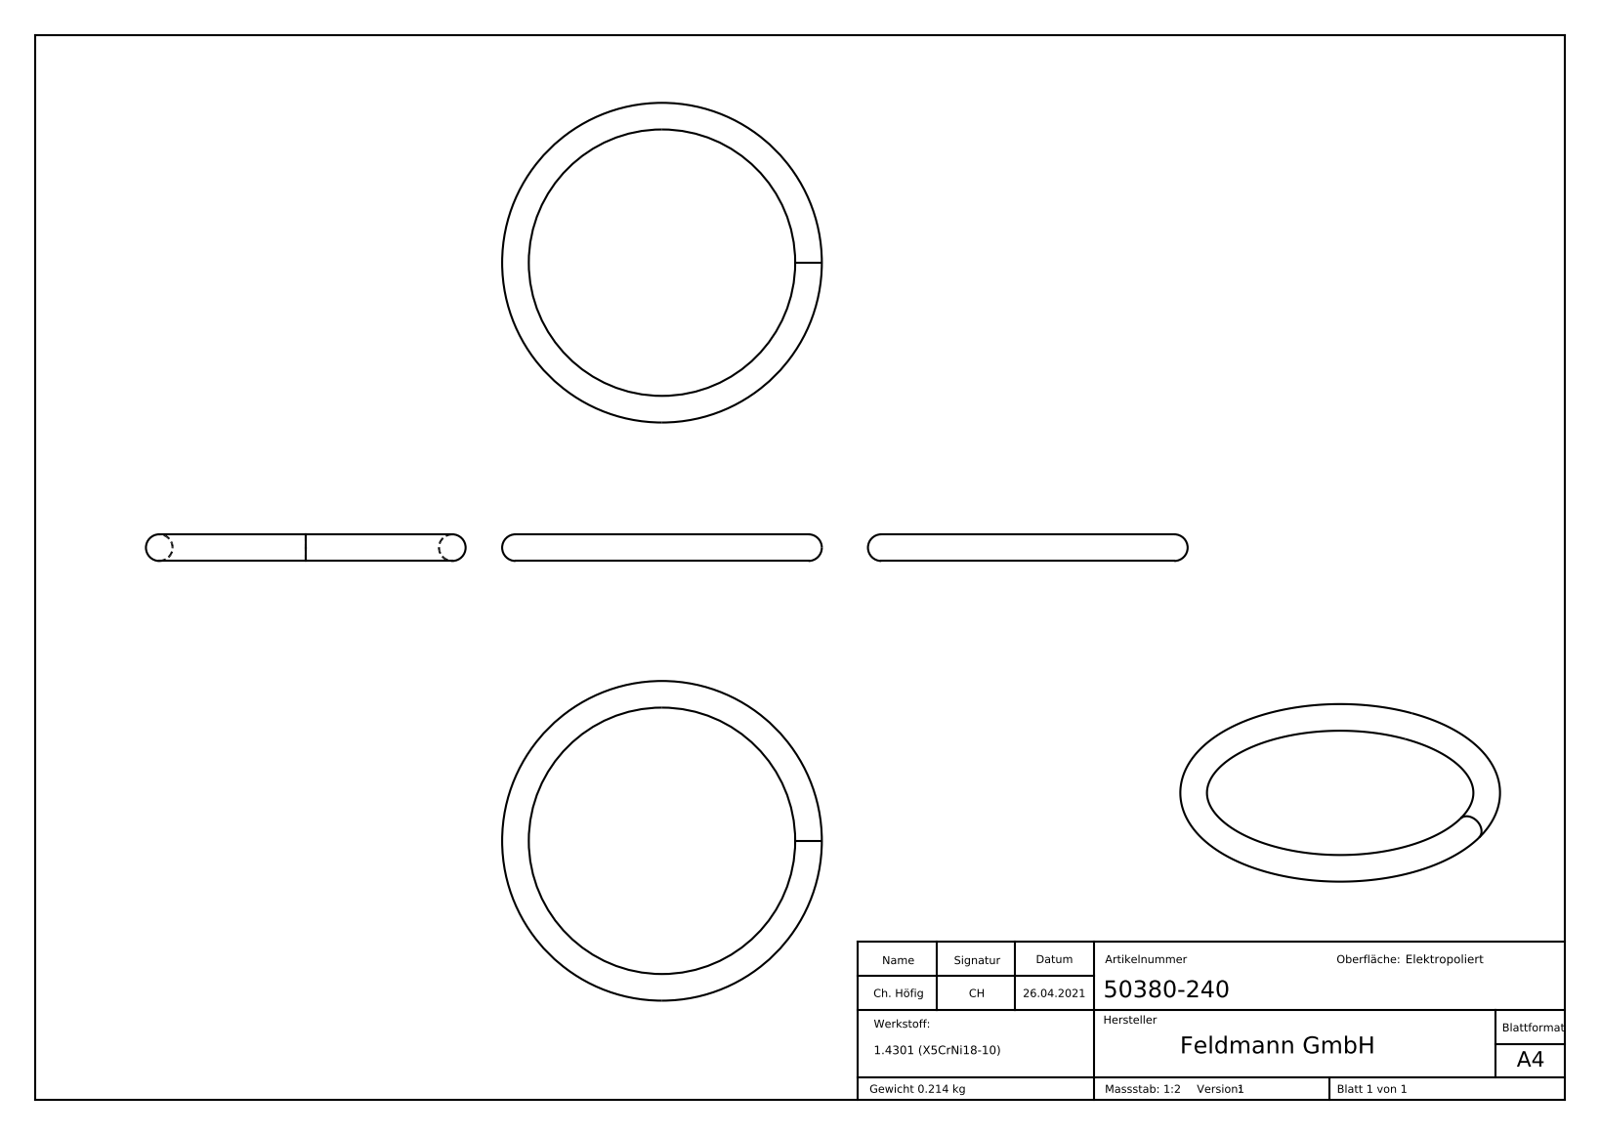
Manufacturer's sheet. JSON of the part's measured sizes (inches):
{"part_name": "50380-240", "step_written_by": "SolidWorks 2018 (CONFIG_CONTROL_DESIGN)", "units": "inches", "bodies": {"solids": 1, "faces": 4, "planar": 0, "cylindrical": 0, "other": 4}, "overall_size": [4.724, 4.724, 0.394], "volume_in3": 1.656, "surface_area_in2": 16.83}
